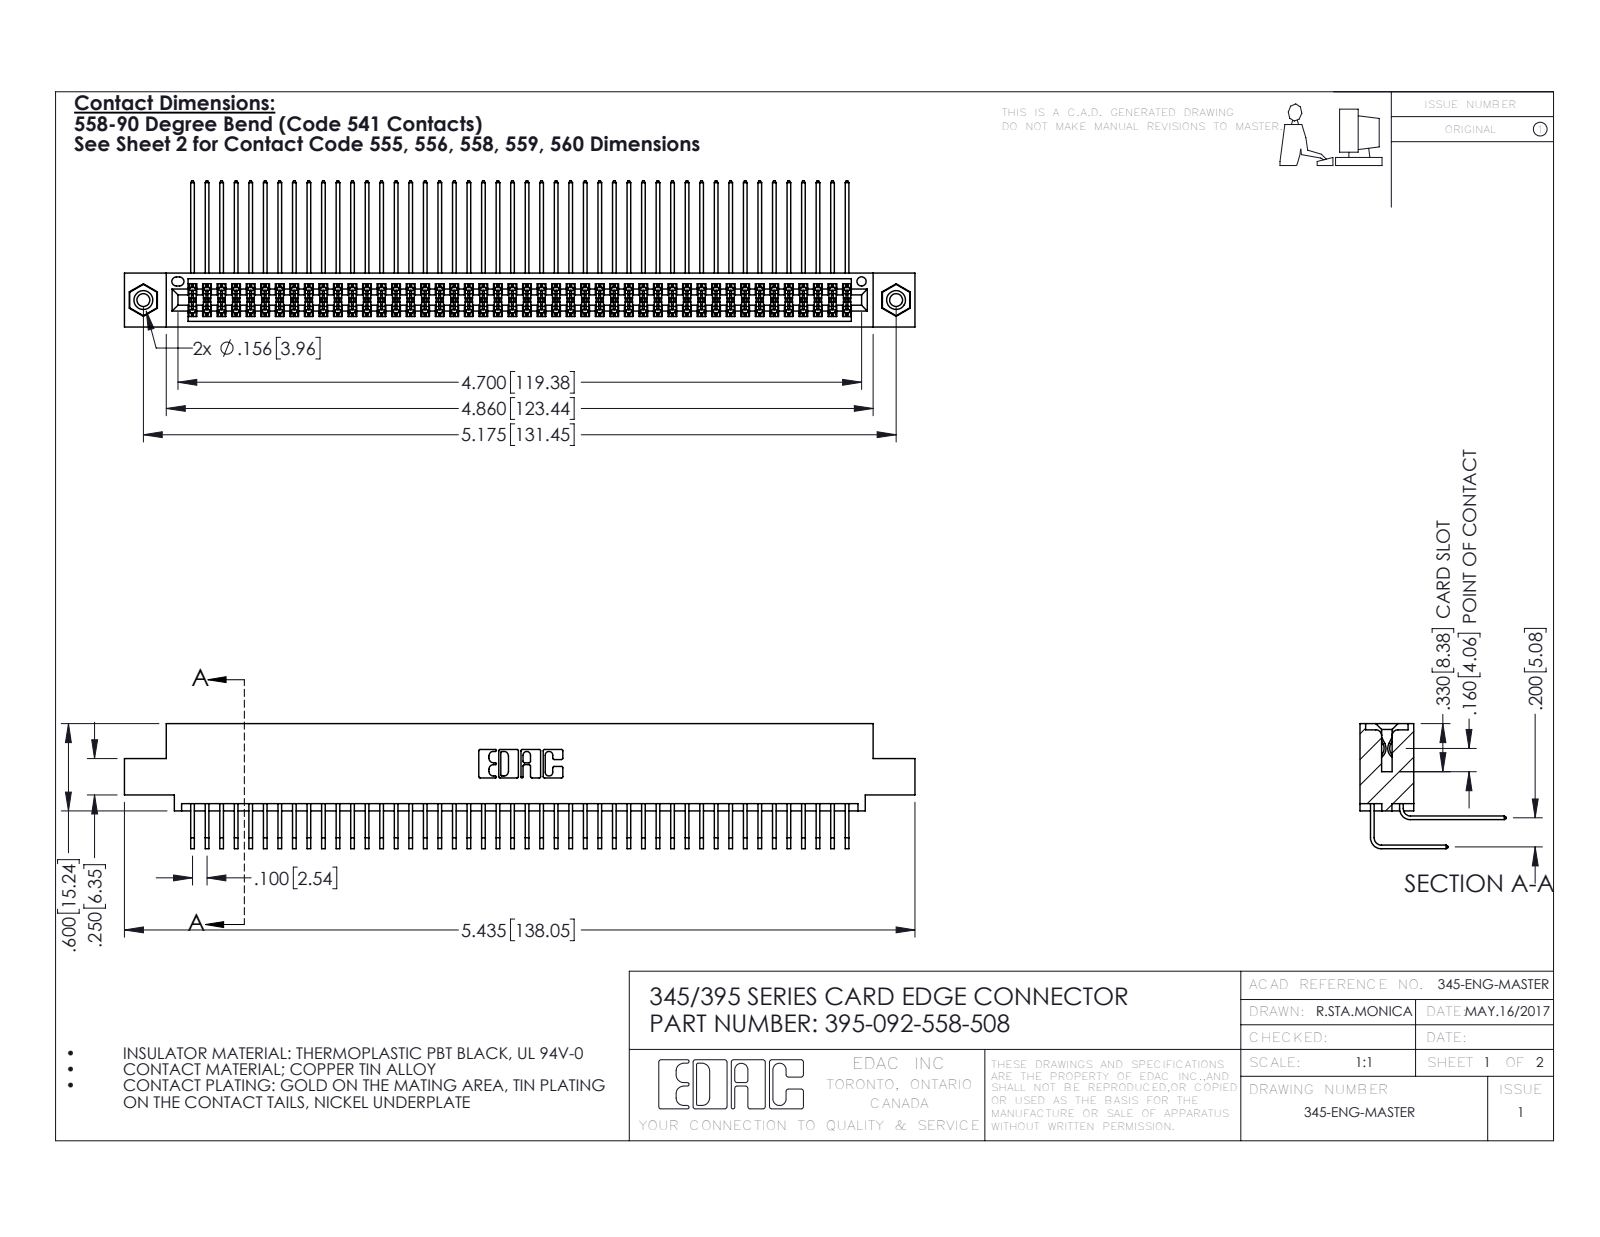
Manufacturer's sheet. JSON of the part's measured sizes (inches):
{"part_name": "395-092-558-508; 345 Part_0.110 Offset - 0.156 Dia-TI; 345-292-001_558 Tail - 2; 345-250-001_345-250-003-102 (+1 more)", "step_written_by": "SolidWorks 2016 (CONFIG_CONTROL_DESIGN)", "units": "inches", "bodies": {"solids": 95, "faces": 4974, "planar": 3336, "cylindrical": 1622, "other": 16}, "overall_size": [5.435, 1.005, 0.859], "volume_in3": 0.848, "surface_area_in2": 36, "round_holes": [[0.089, 2], [0.125, 2], [0.156, 2], [0.064, 1]], "round_bosses_or_shafts": [[0.155, 2]], "partial_cylinders_radius": [[0.006, 139], [0.01, 22], [0.007, 6], [0.031, 6], [0.026, 3], [0.014, 2], [0.019, 2], [0.022, 2]], "face_to_face_distances": [0.072, 0.298, 0.2, 0.37, 0.098, 0.272, 0.025, 0.225, 0.025, 0.175], "hole_center_spacings": [0.27, 4.939, 5.175]}
